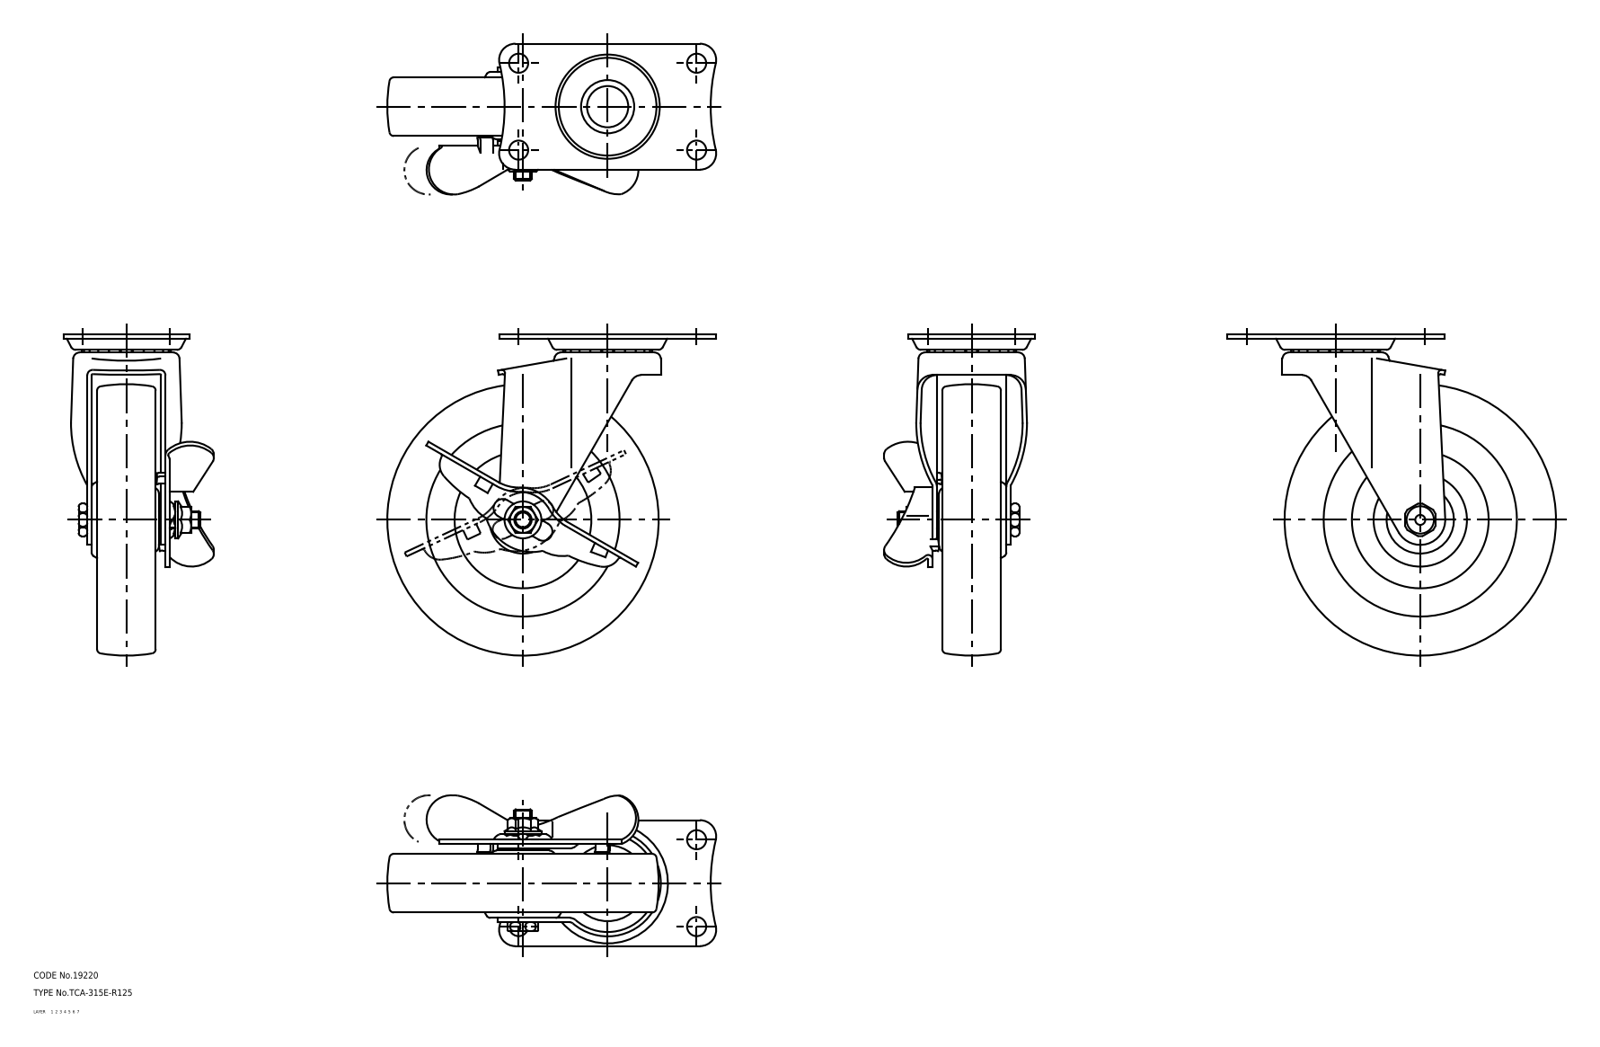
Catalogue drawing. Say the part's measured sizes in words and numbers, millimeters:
The part is named "67133115; 67133128; 67133141; 67133154 (+2 more)". Its 3-D file was written by "CADfix (AUTOMOTIVE_DESIGN)". It is 6 solids with 369 faces: 0 planar, 0 cylindrical and 369 other. Overall it measures 151.5 by 148 by 69.45 millimeters. Its volume is 363 645 cubic millimeters and its surface area 83 062 square millimeters.
